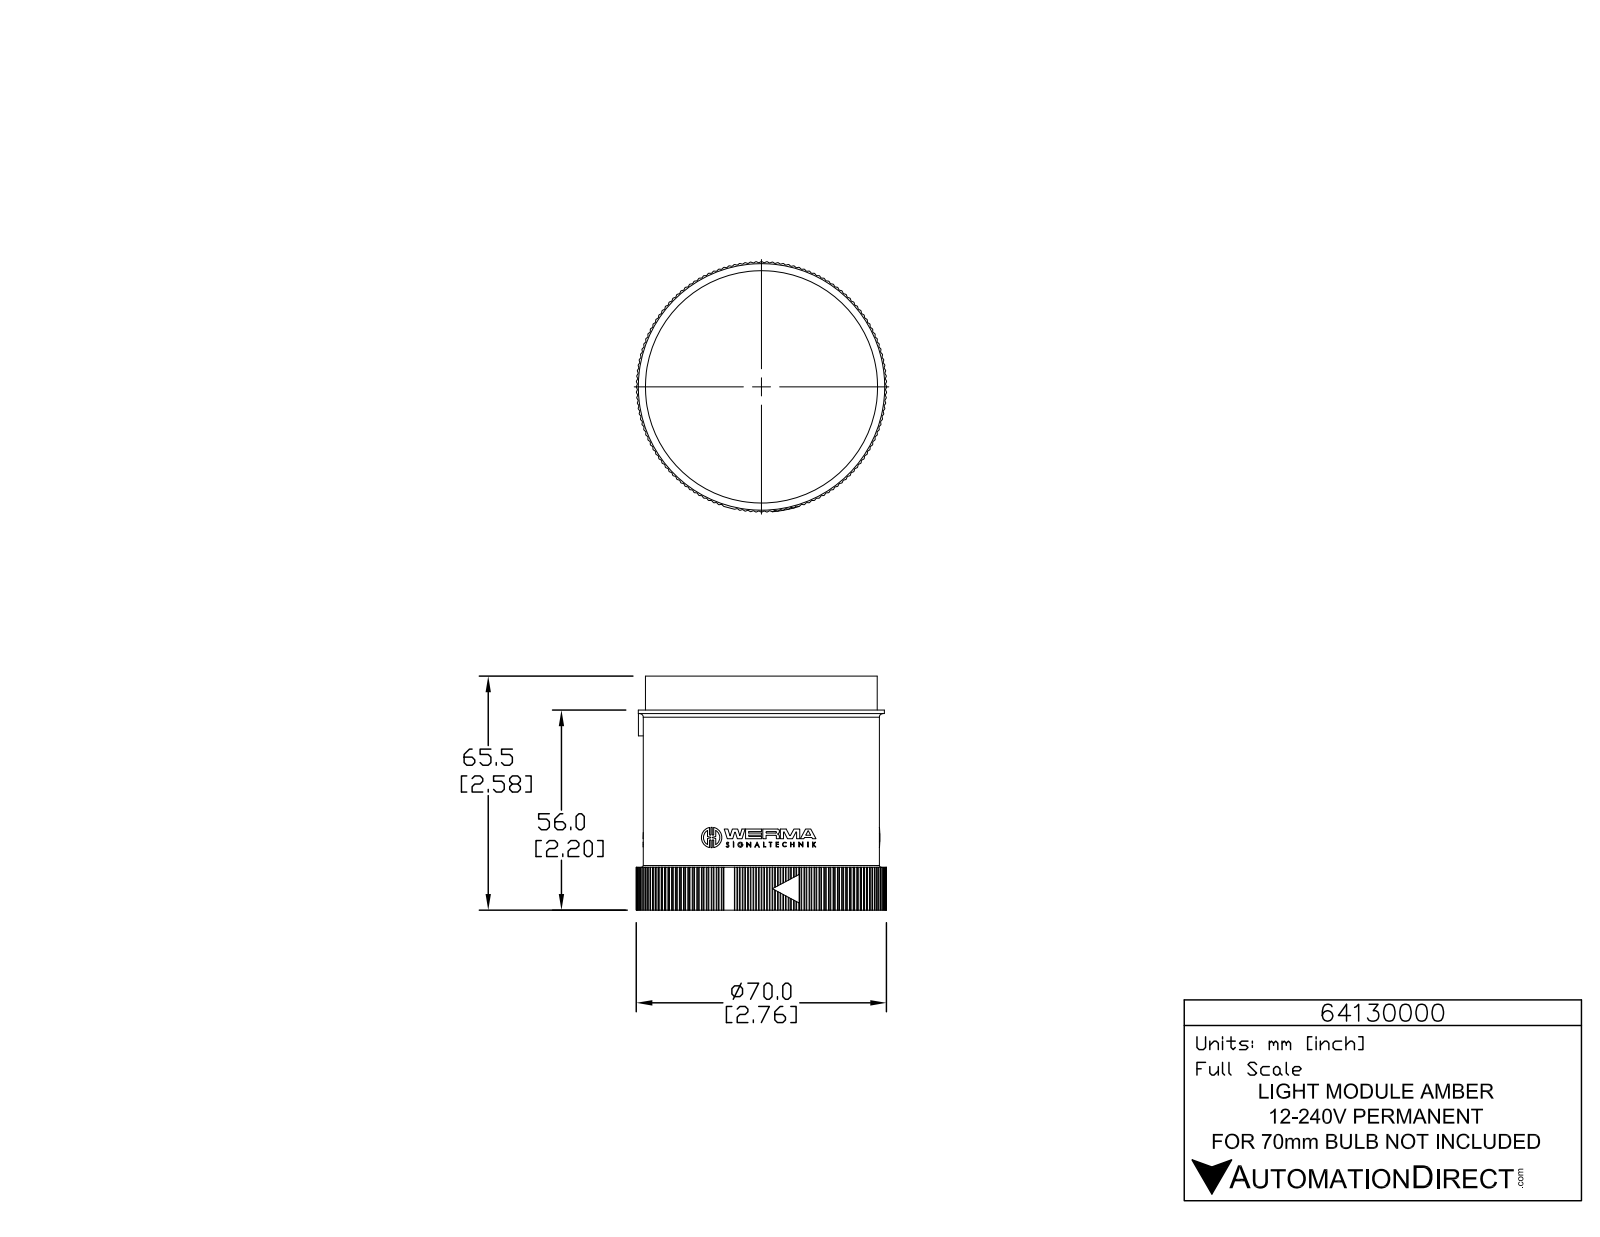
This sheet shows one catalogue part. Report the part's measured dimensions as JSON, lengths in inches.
{"part_name": "64130000", "step_written_by": "SolidWorks 2015 (AUTOMOTIVE_DESIGN)", "units": "inches", "bodies": {"solids": 1, "faces": 1400, "planar": 832, "cylindrical": 563, "other": 5}, "overall_size": [2.762, 2.762, 2.579], "volume_in3": 12.02, "surface_area_in2": 37.48, "round_holes": [[0.039, 3], [2.575, 1]], "round_bosses_or_shafts": [[0.226, 3], [0.056, 3], [2.717, 1], [2.606, 1], [2.559, 1]], "partial_cylinders_radius": [[0.008, 285], [0.008, 6], [0.008, 6], [0.008, 6], [0.131, 6], [0.004, 3], [0.005, 3], [0.008, 3]], "face_to_face_distances": [2.201, 2.451, 0.378, 2.579, 2.205, 1.827, 0.374, 2.452, 0.472, 0.094]}
